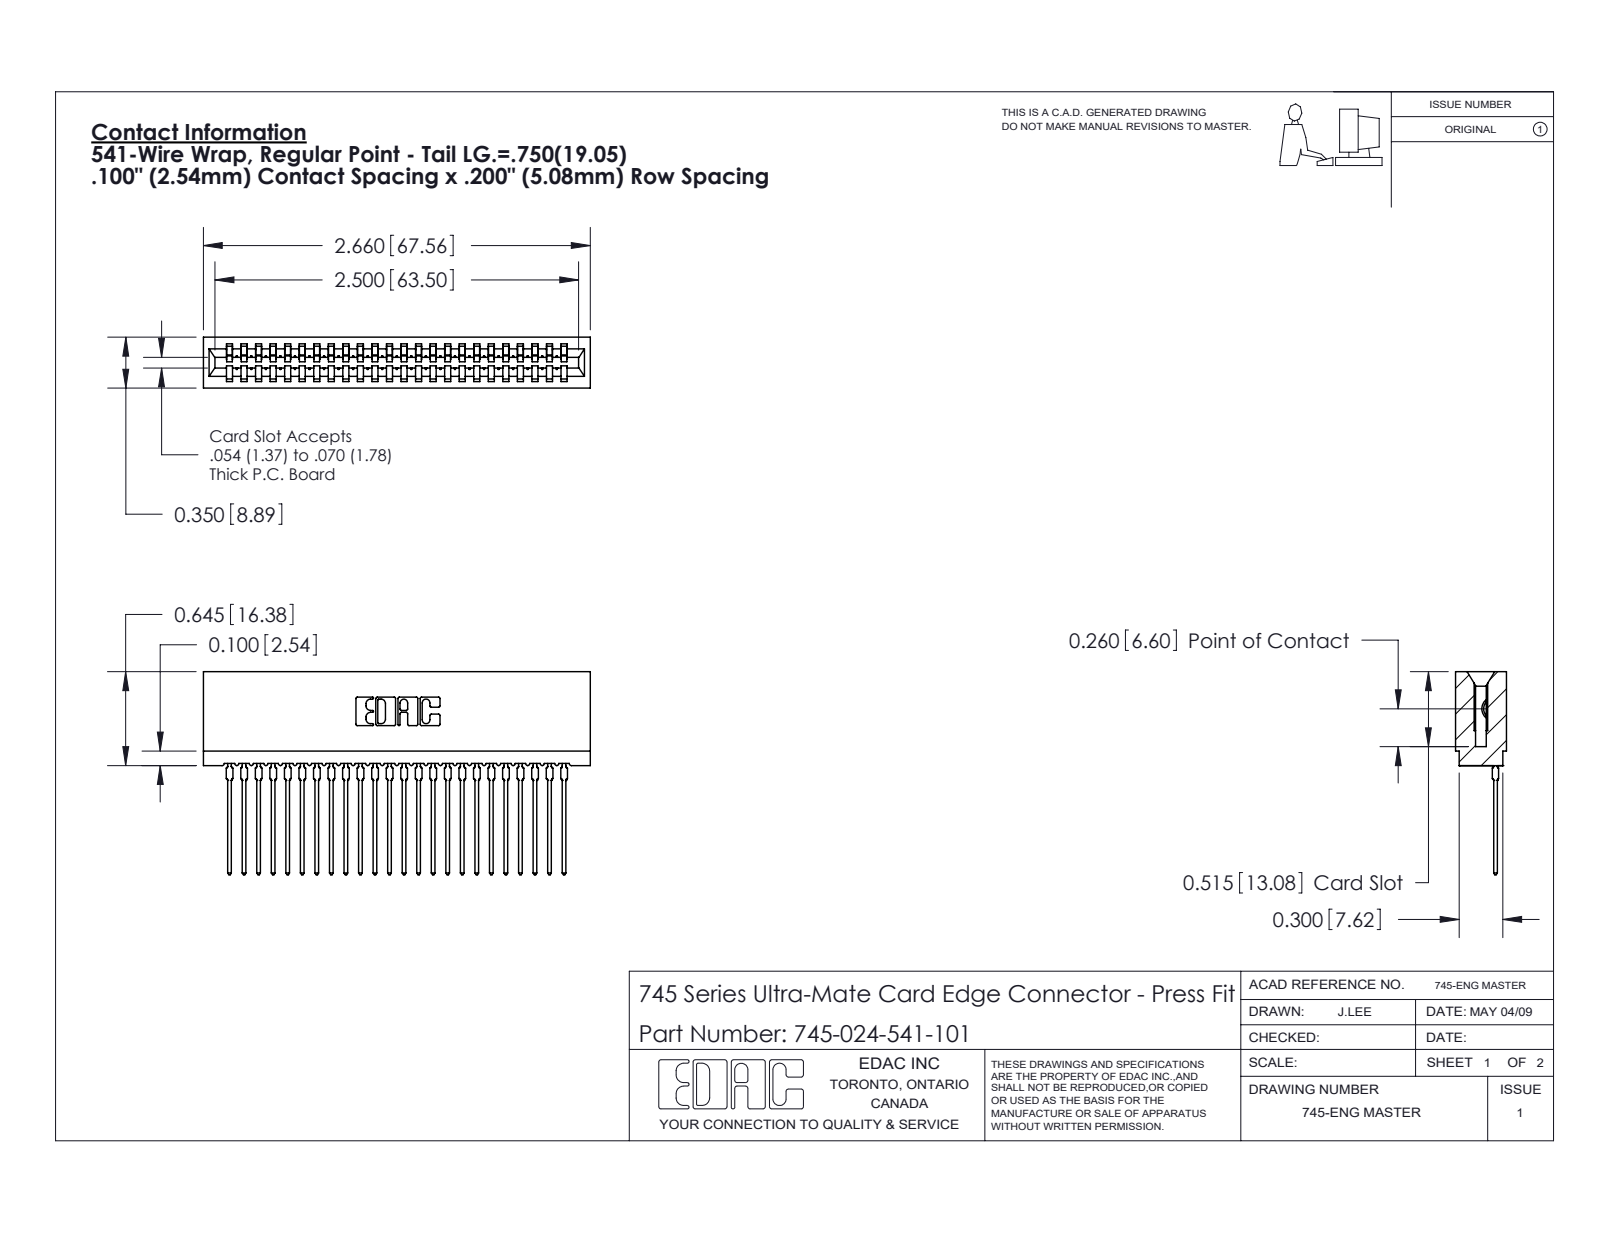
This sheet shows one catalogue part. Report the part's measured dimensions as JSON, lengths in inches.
{"part_name": "745-292-001_541; 745 Part_Insulator Option - 01; 745-024-541-101", "step_written_by": "SolidWorks 2020 (CONFIG_CONTROL_DESIGN)", "units": "inches", "bodies": {"solids": 25, "faces": 2783, "planar": 1663, "cylindrical": 496, "other": 624}, "overall_size": [2.66, 1.396, 0.35], "volume_in3": 0.371, "surface_area_in2": 17.73, "partial_cylinders_radius": [[0.015, 48], [0.021, 48], [0.01, 22], [0.007, 6], [0.031, 6], [0.005, 4], [0.011, 4], [0.026, 3]], "face_to_face_distances": [0.2, 0.1, 0.3, 0.35, 0.4, 0.5, 0.138, 0.212, 0.6, 0.063]}
